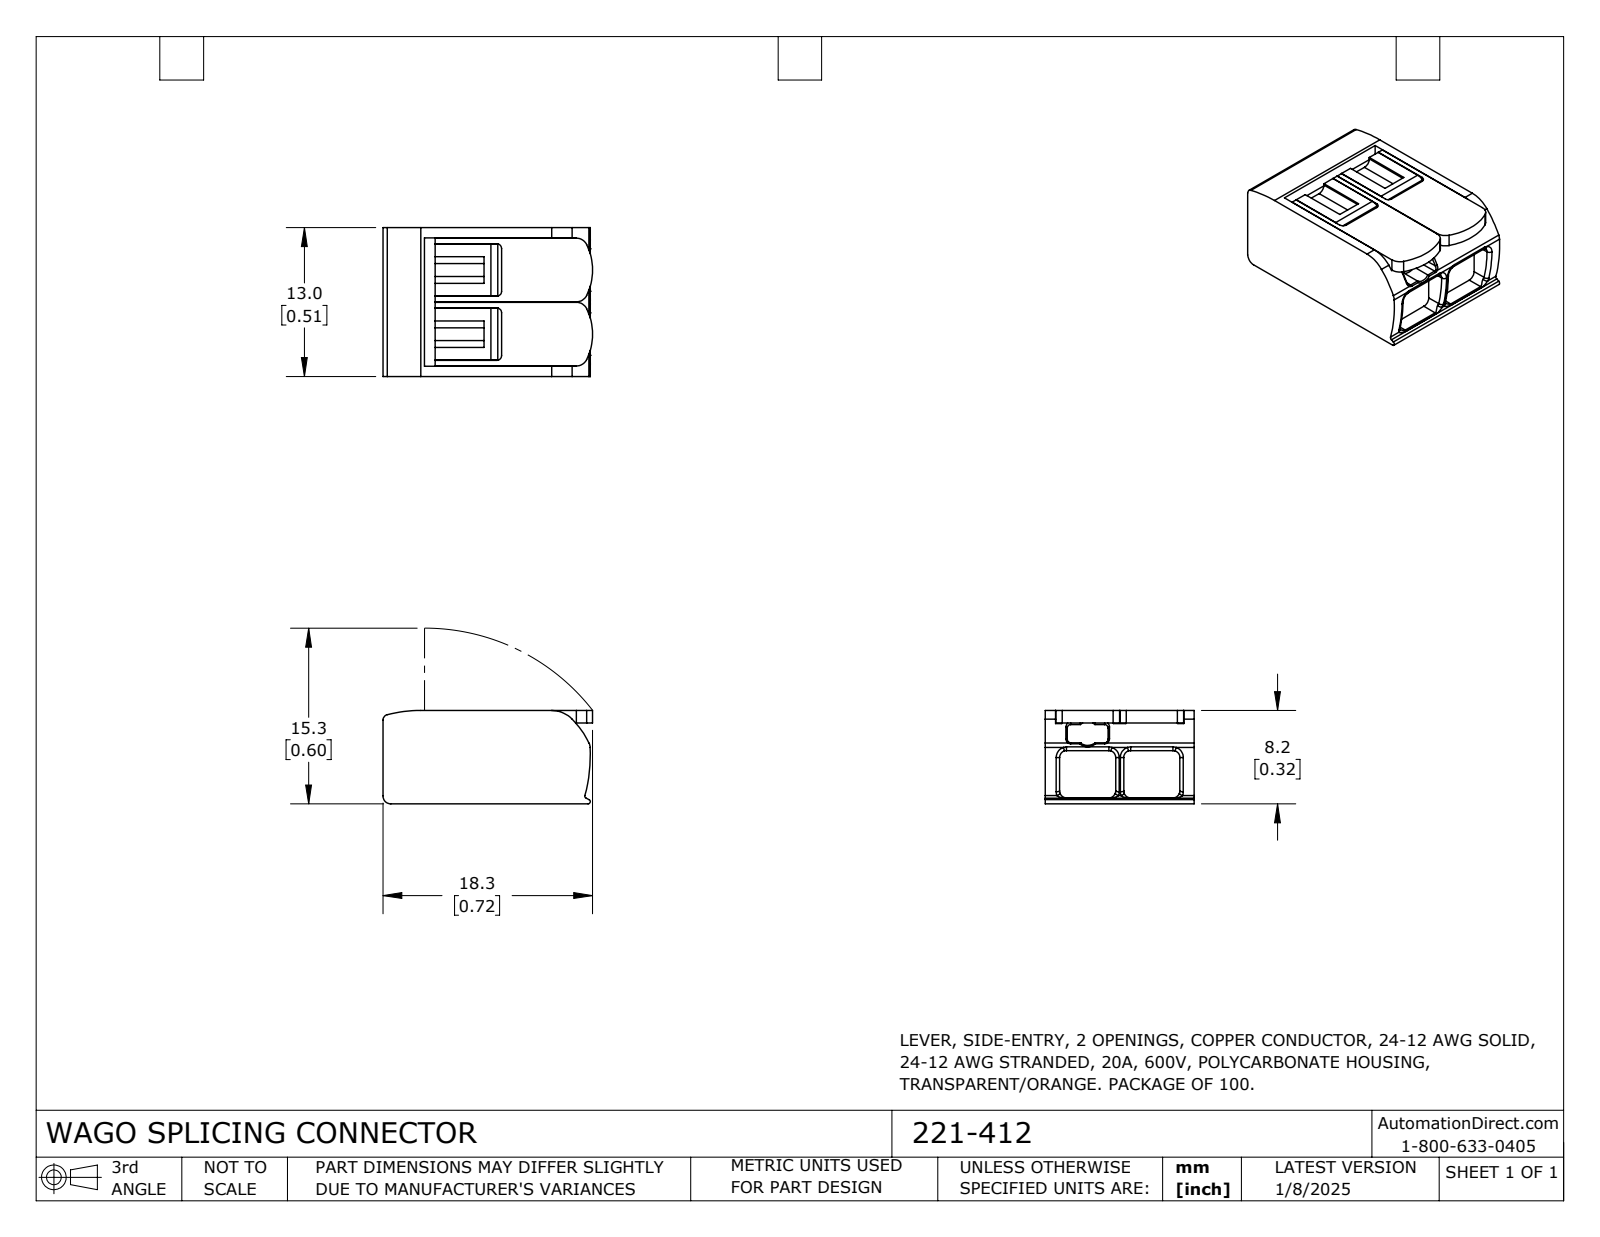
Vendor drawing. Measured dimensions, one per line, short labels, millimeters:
name: 221-412
written by: SolidWorks 2023 (CONFIG_CONTROL_DESIGN)
unit: mm
bodies: 1 solid, 162 faces (70 planar, 61 cylindrical, 31 other)
size: 18.3 × 13 × 8.15
volume: 1 756 mm³; area: 1 290 mm²
rounds: 12× R0.6, 10× R0.3, 6× R1, 4× R0.2, 4× R0.4, 2× R0.13, 2× R5, 1× R0.5
face distances: 8.15, 13, 5.6, 16.2, 5.62, 5.58, 7.05, 1.1, 0.52, 6.52
